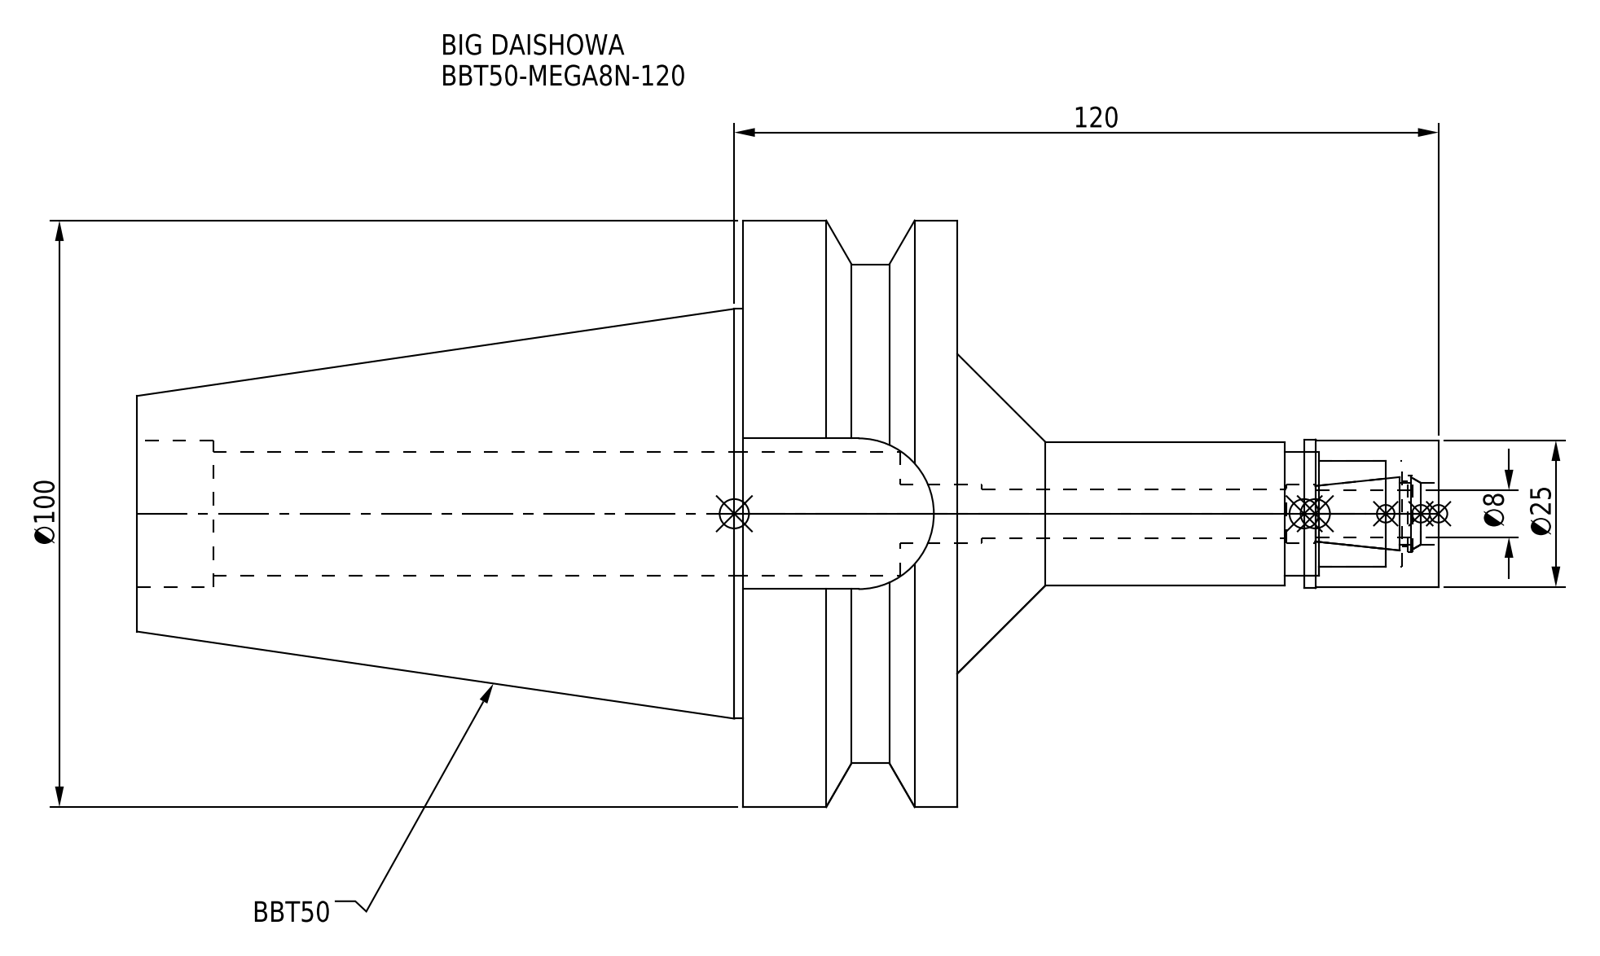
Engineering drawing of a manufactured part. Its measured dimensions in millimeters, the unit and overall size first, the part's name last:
Units: millimetres
Overall size (bounding box): 221.8 × 100 × 100
Round holes (diameter × count): ⌀8.4 ×1, ⌀10 ×1, ⌀10.5 ×1, ⌀11 ×1, ⌀13 ×1, ⌀18 ×1, ⌀21 ×1, ⌀21.2 ×1, ⌀25 ×1
Round bosses / shafts (diameter × count): ⌀100 ×1, ⌀85 ×1, ⌀69.85 ×1, ⌀25.3 ×1, ⌀24.5 ×1
Partial cylindrical surfaces — rounded edges, fillets, slot ends (radius × count): R12.85 ×1
Main face-to-face distances: 36.5, 139.8, 103.3, 70.8, 25.7, 82, 118.5, 221.8, 91.8, 9.8
Volume: 495 439 mm³ · Surface area: 65 205 mm²
Bodies: 2 solids, 79 faces (23 planar, 42 cylindrical, 14 other)
Part name (STEP PRODUCT): MGN8_1.stp; BBT50-MEGA8N-120-080.stp; BBT50-MEGA8N-120; DXF_TEMP_ASSY_ASM_4_ASM.stp (+3 more)
STEP written by: SolidWorks 2019 (CONFIG_CONTROL_DESIGN)
